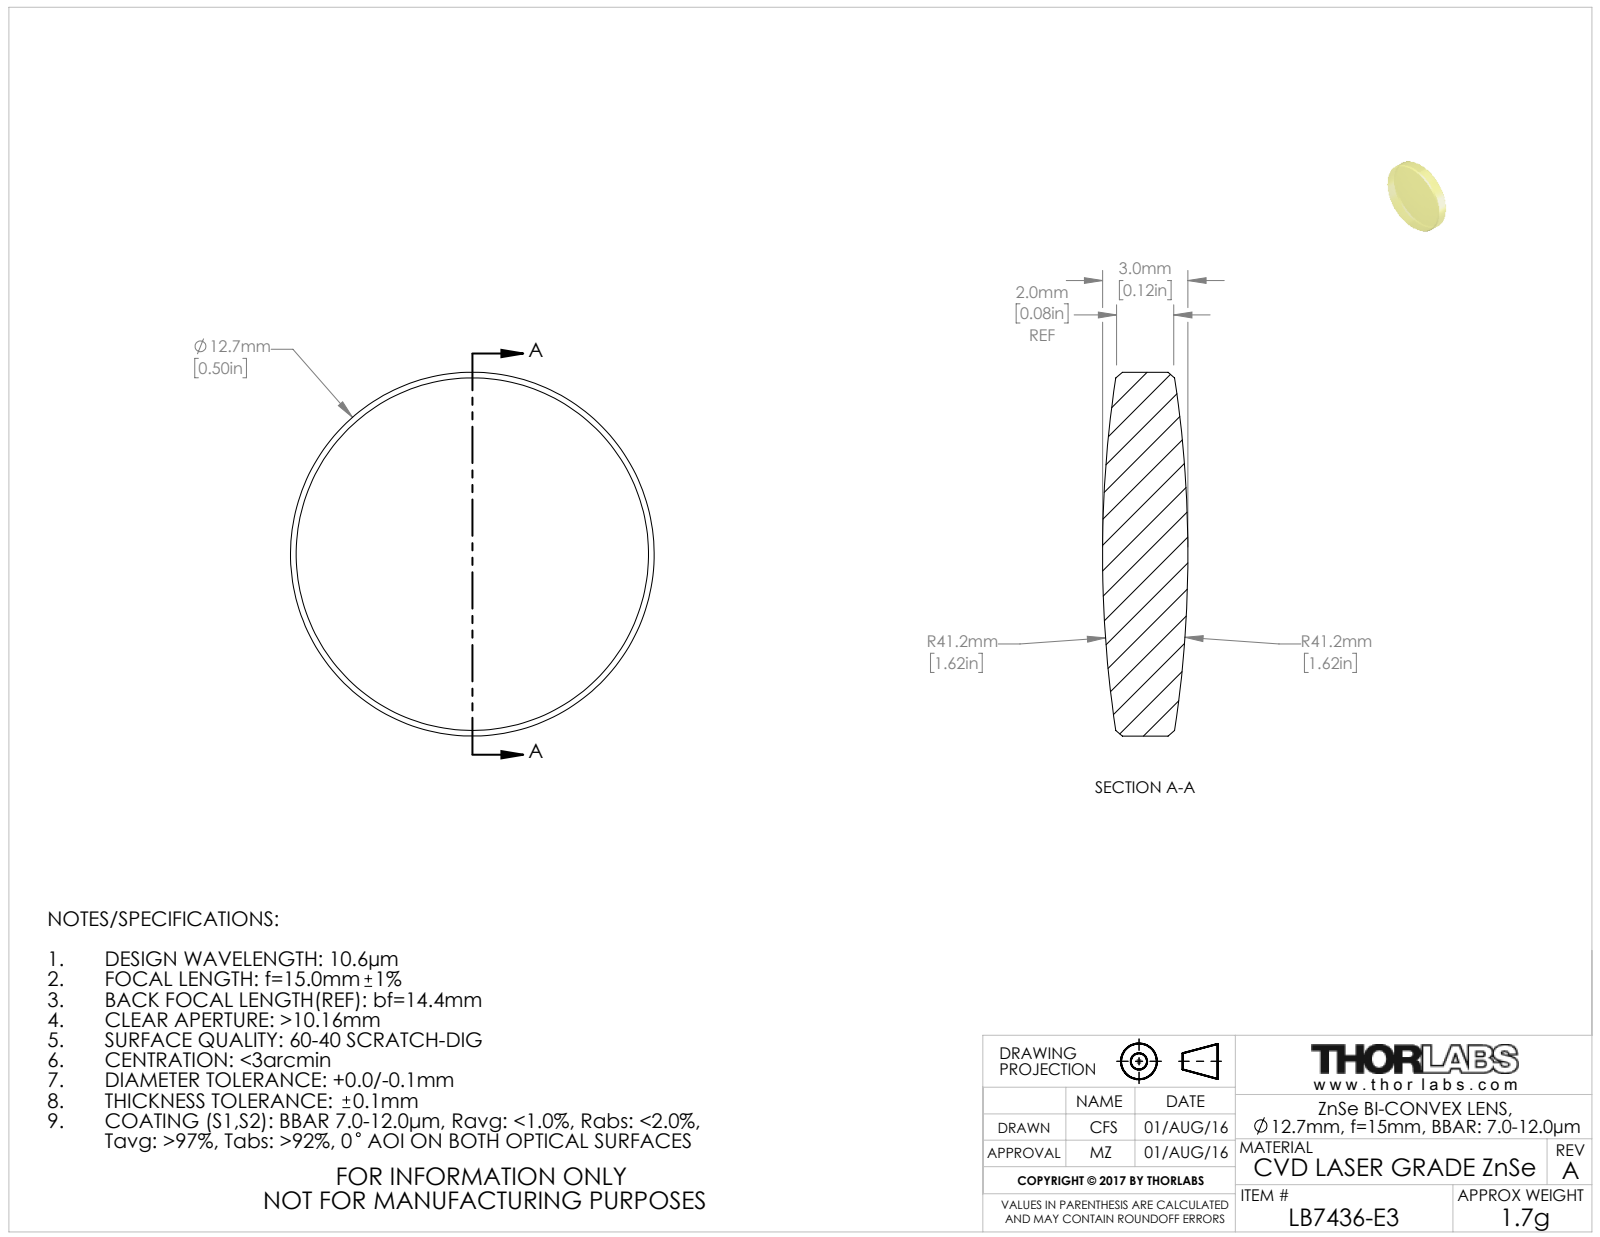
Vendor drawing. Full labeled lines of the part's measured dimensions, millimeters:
Part name (STEP PRODUCT): TTN051875-E0W
STEP written by: SolidWorks 2016 (CONFIG_CONTROL_DESIGN)
Units: millimetres
Bodies: 1 solid, 10 faces (0 planar, 2 cylindrical, 8 other)
Overall size (bounding box): 12.7 × 12.7 × 3
Volume: 310 mm³ · Surface area: 326 mm²
Round bosses / shafts (diameter × count): ⌀12.7 ×1
